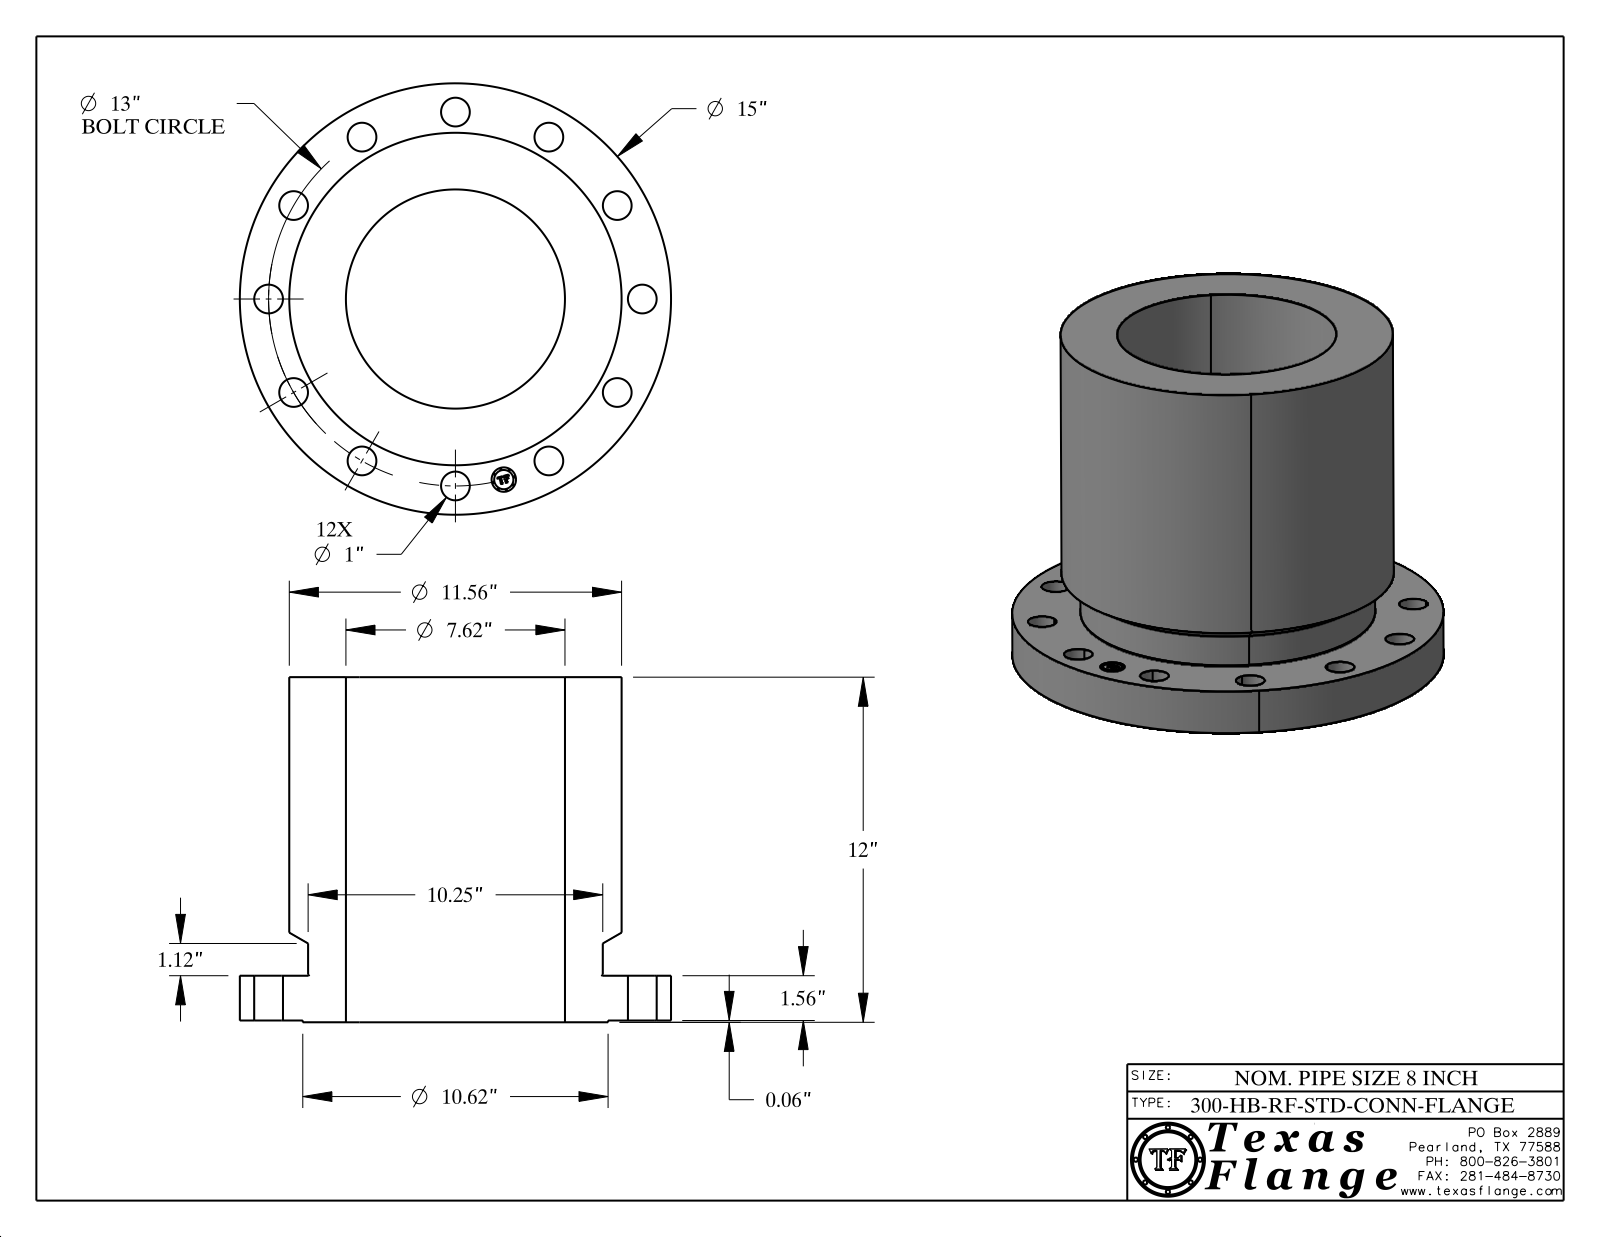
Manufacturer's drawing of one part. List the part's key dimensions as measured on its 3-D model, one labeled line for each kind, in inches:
Part name (STEP PRODUCT): 8-300-HB-RF-STD-CONN-FLANGE
STEP written by: CATIA V5 STEP AP214 (AUTOMOTIVE_DESIGN)
Units: inches
Bodies: 1 solid, 429 faces (369 planar, 54 cylindrical, 6 other)
Overall size (bounding box): 15 × 15 × 12
Volume: 778.8 in³ · Surface area: 1 073 in²
Round holes (diameter × count): ⌀1 ×12, ⌀0.85 ×1, ⌀7.62 ×1
Round bosses / shafts (diameter × count): ⌀0.051 ×8, ⌀15 ×1, ⌀11.56 ×1, ⌀10.62 ×1, ⌀10.25 ×1, ⌀0.67 ×1
Main face-to-face distances: 1.557, 11.937, 10.38, 0.063, 1.62, 12, 1.615, 1.552, 10.385, 0.254
Hole centre spacings: 6.5, 3.365, 9.193, 11.258, 12.557, 13, 1.697, 4.975
